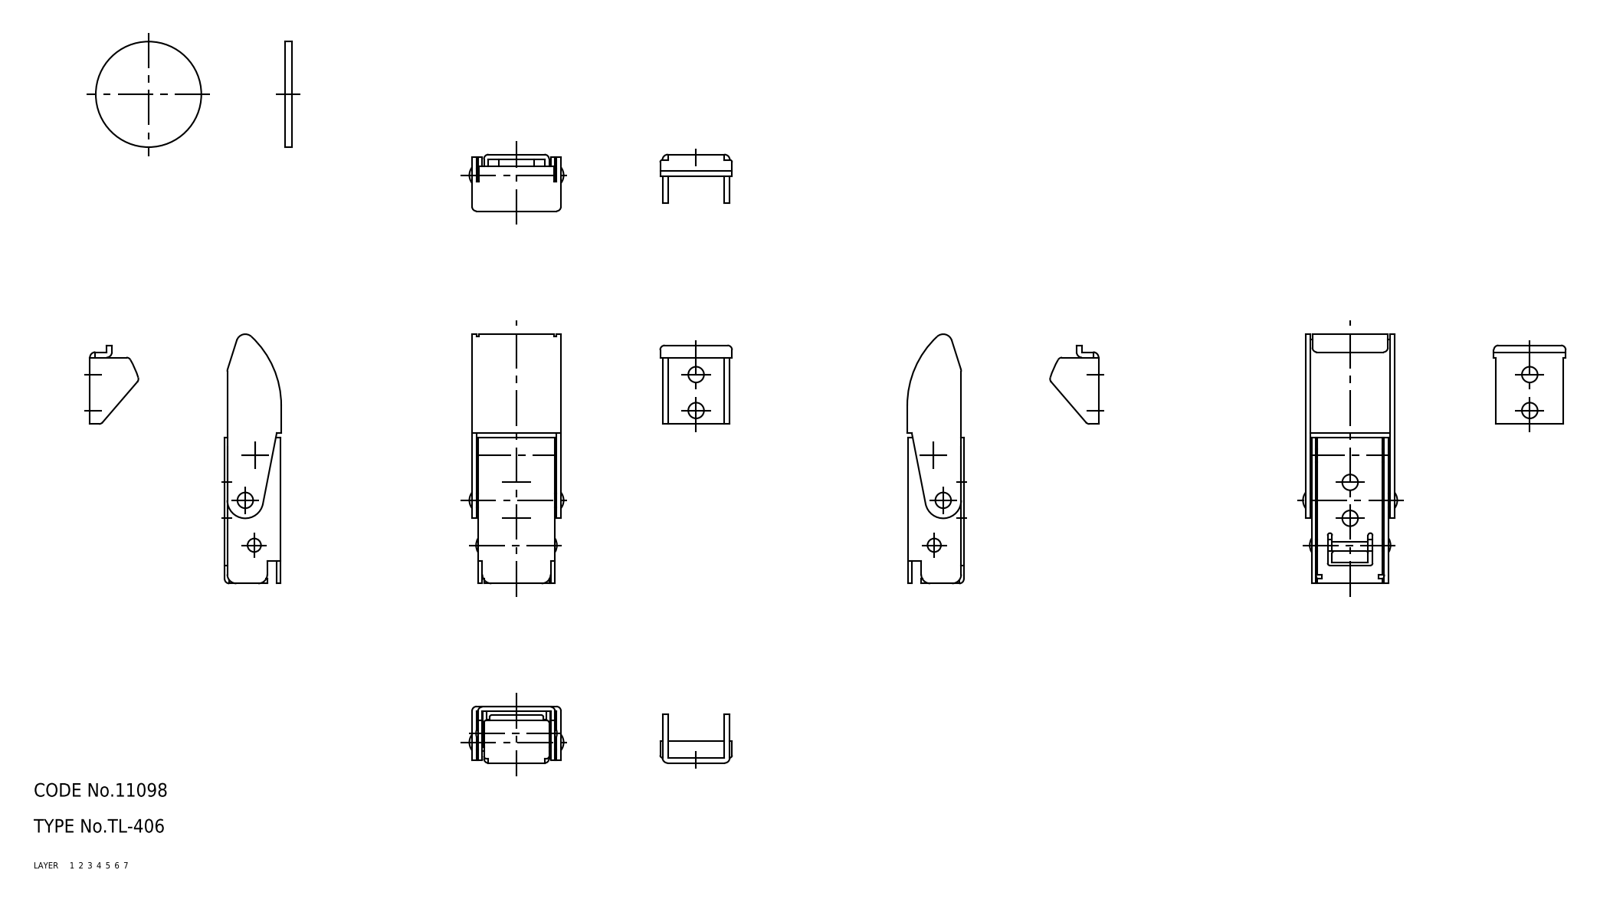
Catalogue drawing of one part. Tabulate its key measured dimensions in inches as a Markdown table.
| quantity | value |
| --- | --- |
| part name | lever; arm; base; keeper (+1 more) |
| STEP written by | SolidWorks 2015 (AUTOMOTIVE_DESIGN) |
| units | inches |
| bodies | 4 solids, 245 faces (126 planar, 109 cylindrical, 10 other) |
| overall size | 2.185 × 0.827 × 0.496 |
| volume | 0.263 in³ |
| surface area | 14.05 in² |
| round holes (diameter × count) | 0.138 × 4, 0.126 × 2, 0.197 × 1 |
| round bosses / shafts (diameter × count) | 0.118 × 2, 0.189 × 1, 0.098 × 1 |
| partial cylindrical surfaces (radius × count) | 0.039 × 20, 0.02 × 13, 0.079 × 7, 0.031 × 4, 0.047 × 4, 0.157 × 2, 0.012 × 1, 0.043 × 1 |
| main face-to-face distances | 0.039, 0.051, 0.689, 0.091, 0.638, 0.453, 0.74, 0.728, 0.65, 0.492 |
| hole center spacings | 0.315, 0.945, 0.403, 0.63, 1.26 |
